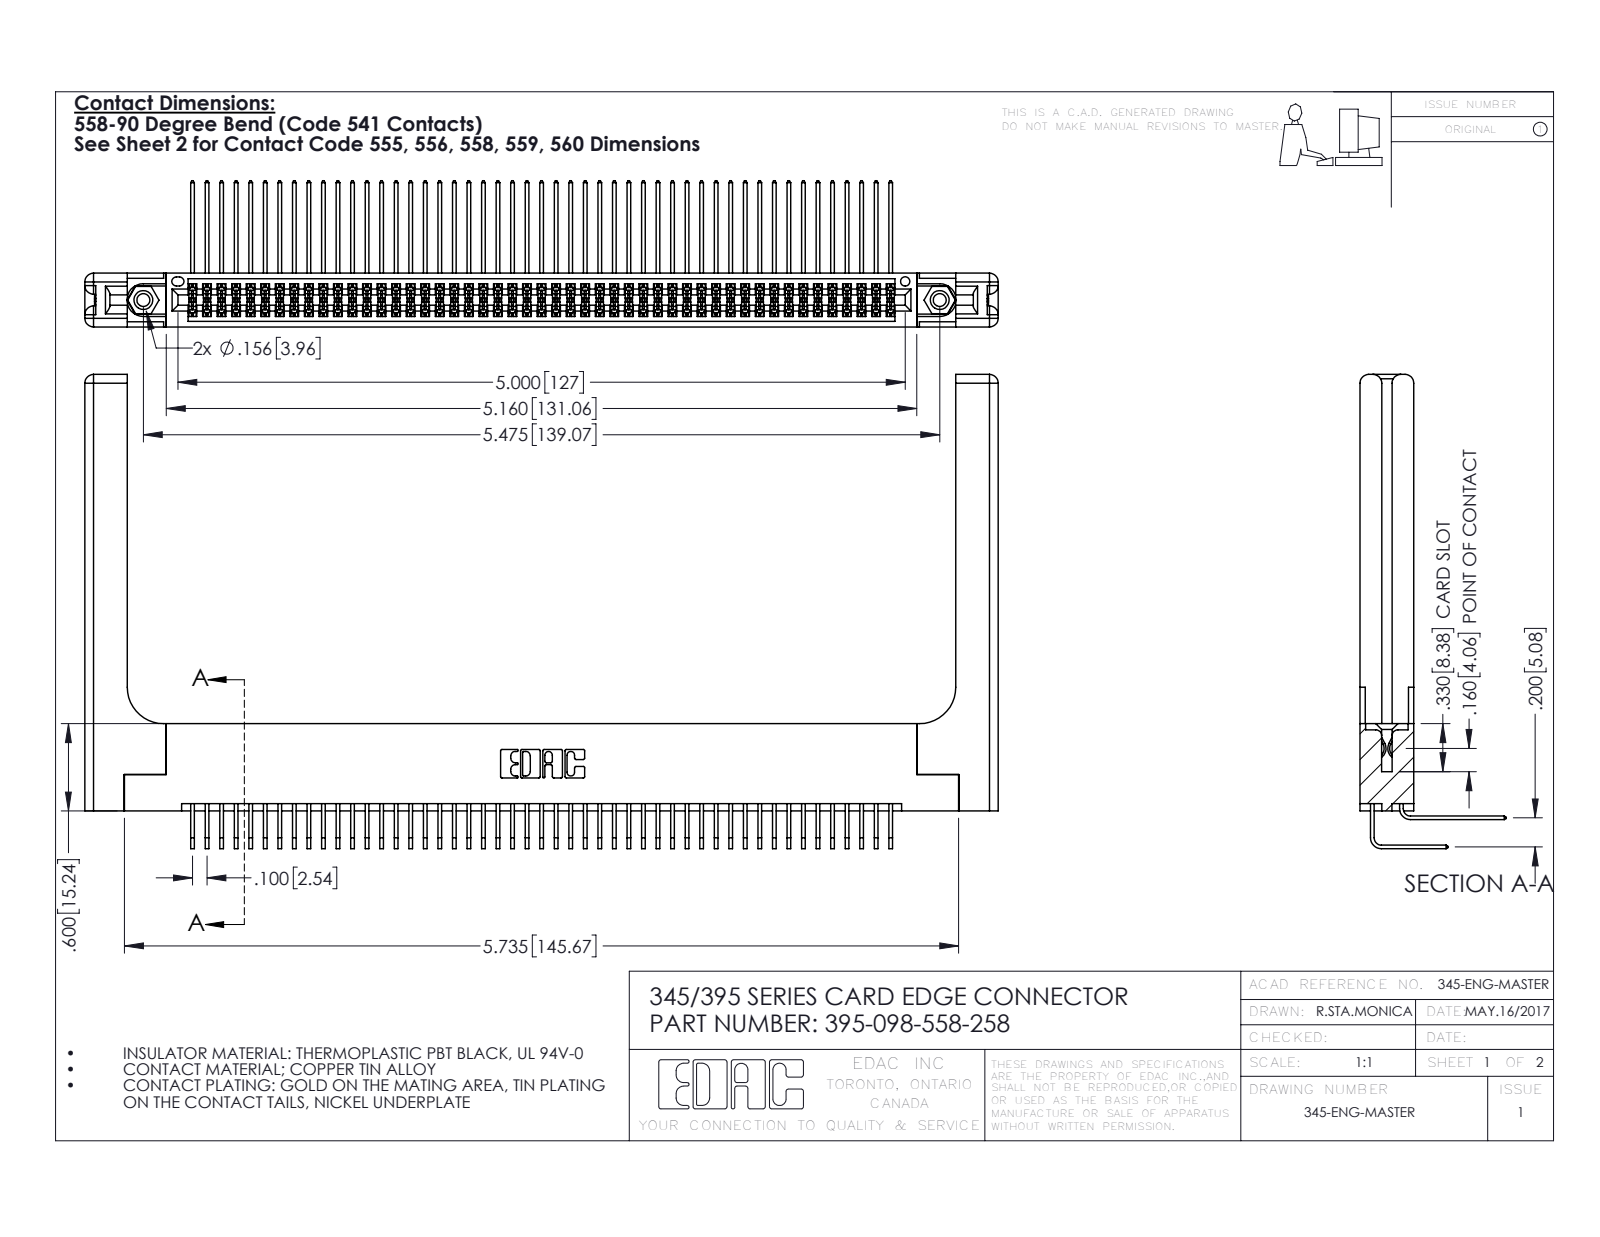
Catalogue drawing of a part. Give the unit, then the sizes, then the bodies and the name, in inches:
Units: inches
Overall size (bounding box): 6.279 × 3.259 × 1.005
Round holes (diameter × count): ⌀0.089 ×2, ⌀0.125 ×2, ⌀0.156 ×2, ⌀0.064 ×1
Round bosses / shafts (diameter × count): ⌀0.155 ×2
Partial cylindrical surfaces — rounded edges, fillets, slot ends (radius × count): R0.006 ×148, R0.01 ×22, R0.06 ×16, R0.007 ×6, R0.031 ×6, R0.026 ×3, R0.014 ×2, R0.019 ×2
Main face-to-face distances: 0.072, 0.298, 0.37, 0.2, 0.098, 0.272, 0.025, 0.225, 0.148, 0.15
Hole centre spacings: 0.27, 5.239, 5.475
Volume: 1.501 in³ · Surface area: 49.11 in²
Bodies: 103 solids, 5478 faces (3658 planar, 1760 cylindrical, 60 other)
Part name (STEP PRODUCT): 345-292-001_558 559 Tail - 1; 345 Part_Flush Mounting Lugs - 0.156 Dia-TH; 345-292-001_558 Tail - 2; 395-098-558-258 (+2 more)
STEP written by: SolidWorks 2016 (CONFIG_CONTROL_DESIGN)
